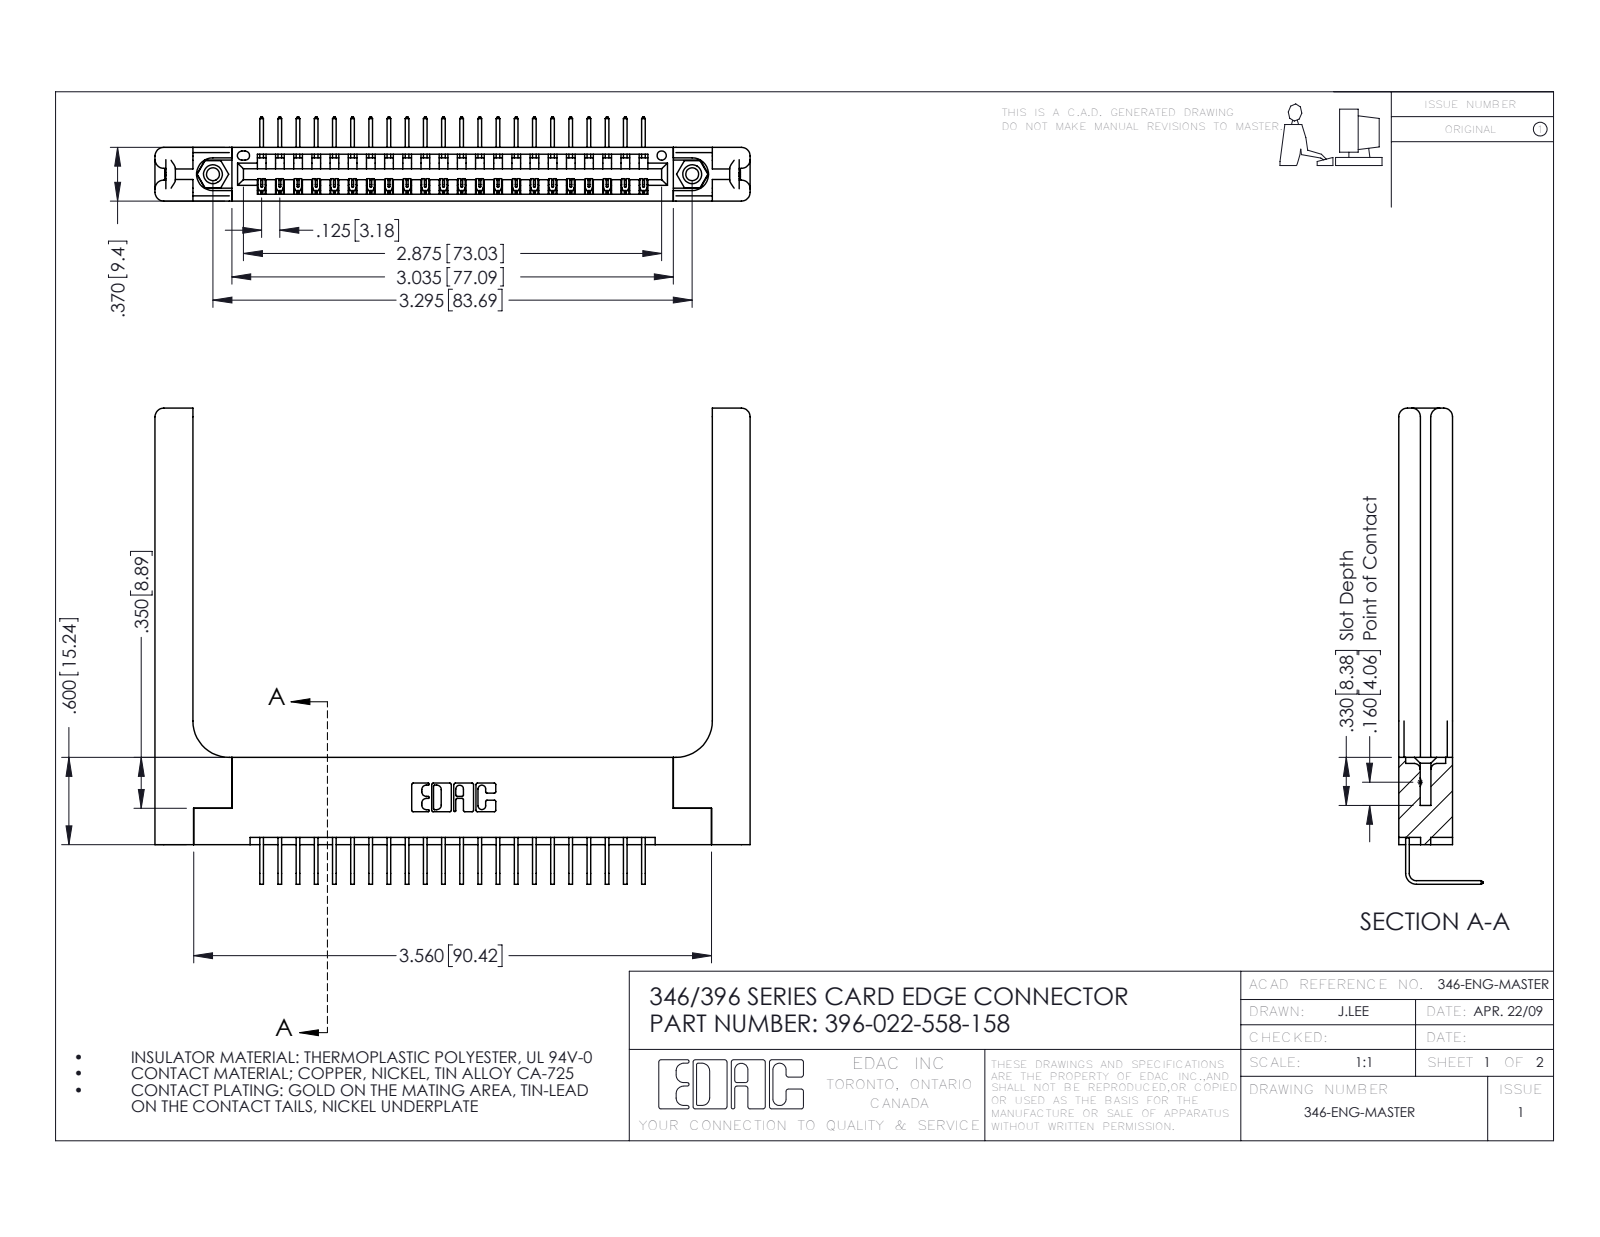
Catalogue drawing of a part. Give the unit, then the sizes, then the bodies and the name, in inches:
Units: inches
Overall size (bounding box): 4.091 × 3.273 × 0.58
Round holes (diameter × count): ⌀0.089 ×2, ⌀0.125 ×2, ⌀0.156 ×2, ⌀0.064 ×1
Round bosses / shafts (diameter × count): ⌀0.155 ×2
Partial cylindrical surfaces — rounded edges, fillets, slot ends (radius × count): R0.006 ×44, R0.01 ×22, R0.06 ×16, R0.007 ×6, R0.031 ×6, R0.026 ×3, R0.03 ×2, R0.031 ×2
Main face-to-face distances: 0.37, 0.072, 0.322, 0.15, 0.048, 0.148, 0.25, 0.025, 0.298, 0.22
Hole centre spacings: 0.246, 3.087, 3.295
Volume: 1.062 in³ · Surface area: 27.5 in²
Bodies: 27 solids, 1698 faces (1148 planar, 490 cylindrical, 60 other)
Part name (STEP PRODUCT): 345-250-001_345-250-001-102; 346-220-058_345-220-058; 346 Part_Flush Mounting Lugs - 0.156 Dia-TH; 396-022-558-158 (+1 more)
STEP written by: SolidWorks 2016 (CONFIG_CONTROL_DESIGN)
